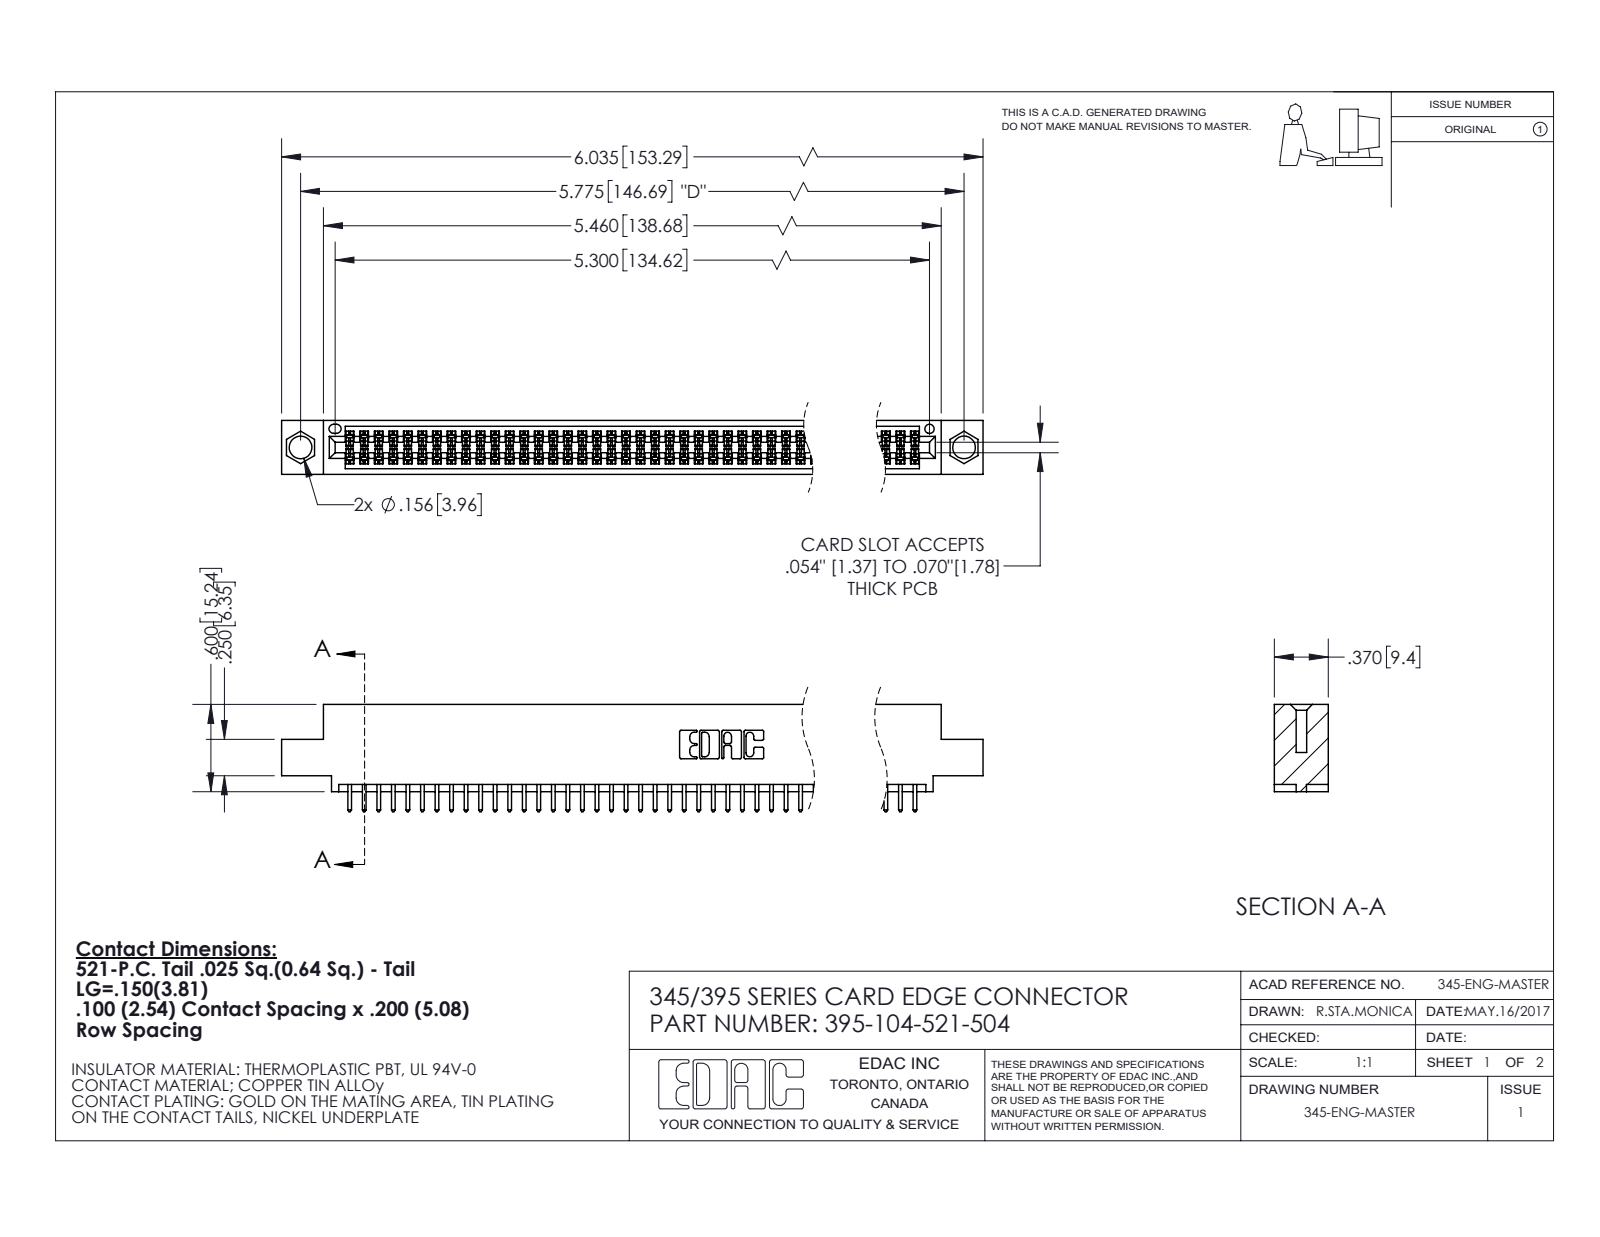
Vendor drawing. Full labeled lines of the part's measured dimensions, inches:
Part name (STEP PRODUCT): 345 Part_0.110 Offset - 0.156 Dia-TI; 345-292-001_345-293-121; 395-104-521-504
STEP written by: SolidWorks 2020 (CONFIG_CONTROL_DESIGN)
Units: inches
Bodies: 105 solids, 5344 faces (3530 planar, 1814 cylindrical, 0 other)
Overall size (bounding box): 6.035 × 0.737 × 0.37
Volume: 0.901 in³ · Surface area: 33.61 in²
Round holes (diameter × count): ⌀0.156 ×2, ⌀0.064 ×1
Partial cylindrical surfaces — rounded edges, fillets, slot ends (radius × count): R0.006 ×156, R0.01 ×104, R0.01 ×22, R0.007 ×6, R0.031 ×6, R0.026 ×3, R0.014 ×2, R0.019 ×2
Main face-to-face distances: 0.298, 0.072, 0.2, 0.37, 0.098, 0.272, 0.025, 0.225, 0.175, 0.149
Hole centre spacings: 0.27, 5.539, 5.775
